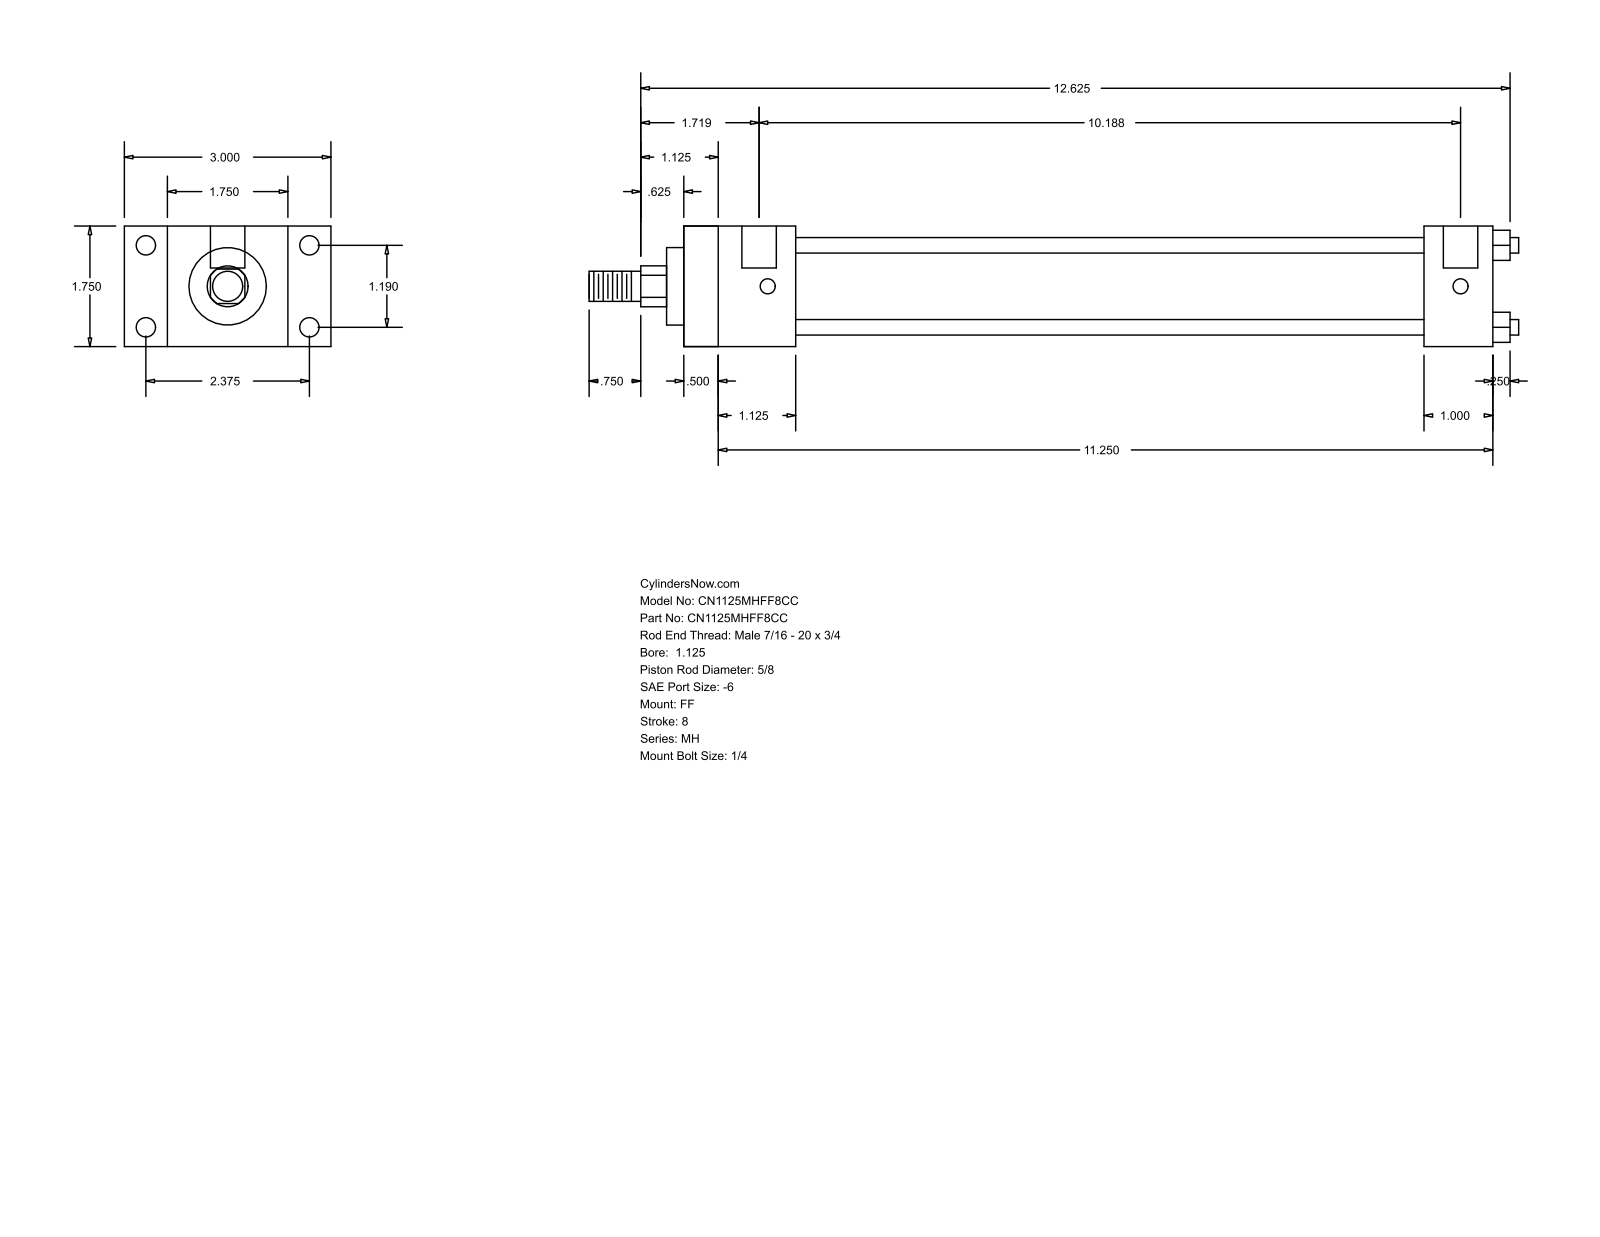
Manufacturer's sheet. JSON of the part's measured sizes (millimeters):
{"part_name": "MH_FF__0112_0.625", "step_written_by": "GSSL Pune (CONFIG_CONTROL_DESIGN)", "units": "millimeters", "bodies": {"solids": 0, "faces": 92, "planar": 64, "cylindrical": 28, "other": 0}, "overall_size": [342.9, 76.2, 44.45], "round_holes": [[5.56, 4], [7.14, 4], [12.7, 2]], "round_bosses_or_shafts": [[5.71, 4], [34.92, 1], [28.57, 1], [15.88, 1], [11.11, 1]], "partial_cylinders_radius": [[7.54, 1]], "face_to_face_distances": [44.46, 298.44, 12.69, 285.75, 15.87, 28.58, 60.33, 41.27, 273.05, 260.36], "hole_center_spacings": [30.22, 60.32, 67.47, 255.59, 3.17, 258.76]}
